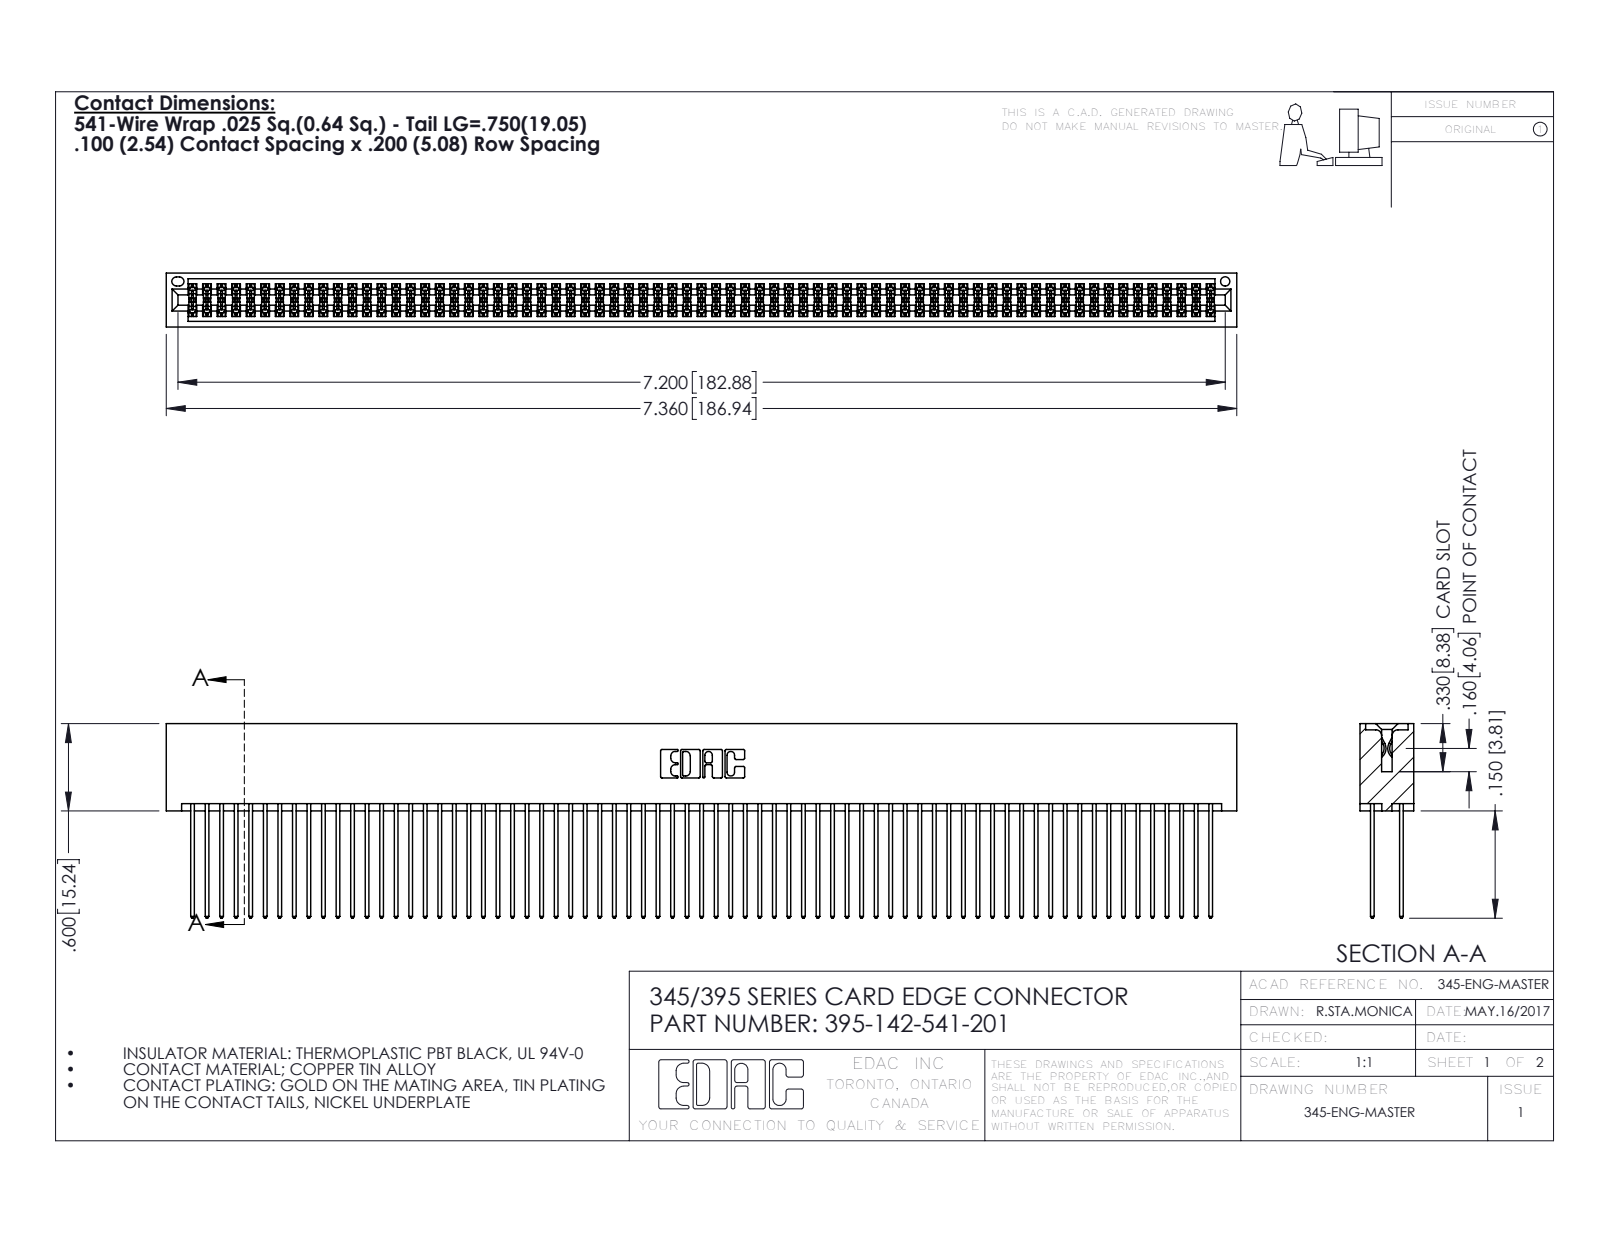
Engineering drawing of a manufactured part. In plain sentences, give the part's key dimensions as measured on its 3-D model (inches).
The part is named "345 Part_No Mounting Lugs; 395-142-541-201; 345-292-001_345-293-141". Its 3-D file was written by "SolidWorks 2016 (CONFIG_CONTROL_DESIGN)". It is 143 solids with 7218 faces: 4762 planar, 2456 cylindrical and 0 other. Overall it measures 7.36 by 1.337 by 0.37 inches. Its volume is 1.212 cubic inches and its surface area 52.78 square inches. Round holes: 1 of diameter 0.064. Partial cylindrical surfaces (rounded edges, fillets, slot ends): 213 of radius 0.006, 142 of radius 0.01, 22 of radius 0.01, 6 of radius 0.007, 6 of radius 0.031, 3 of radius 0.026, 2 of radius 0.014, 2 of radius 0.019. The main face-to-face distances are 0.298, 0.072, 0.2, 0.098, 0.272, 0.025, 0.225, 0.37, 0.175, 0.149.
